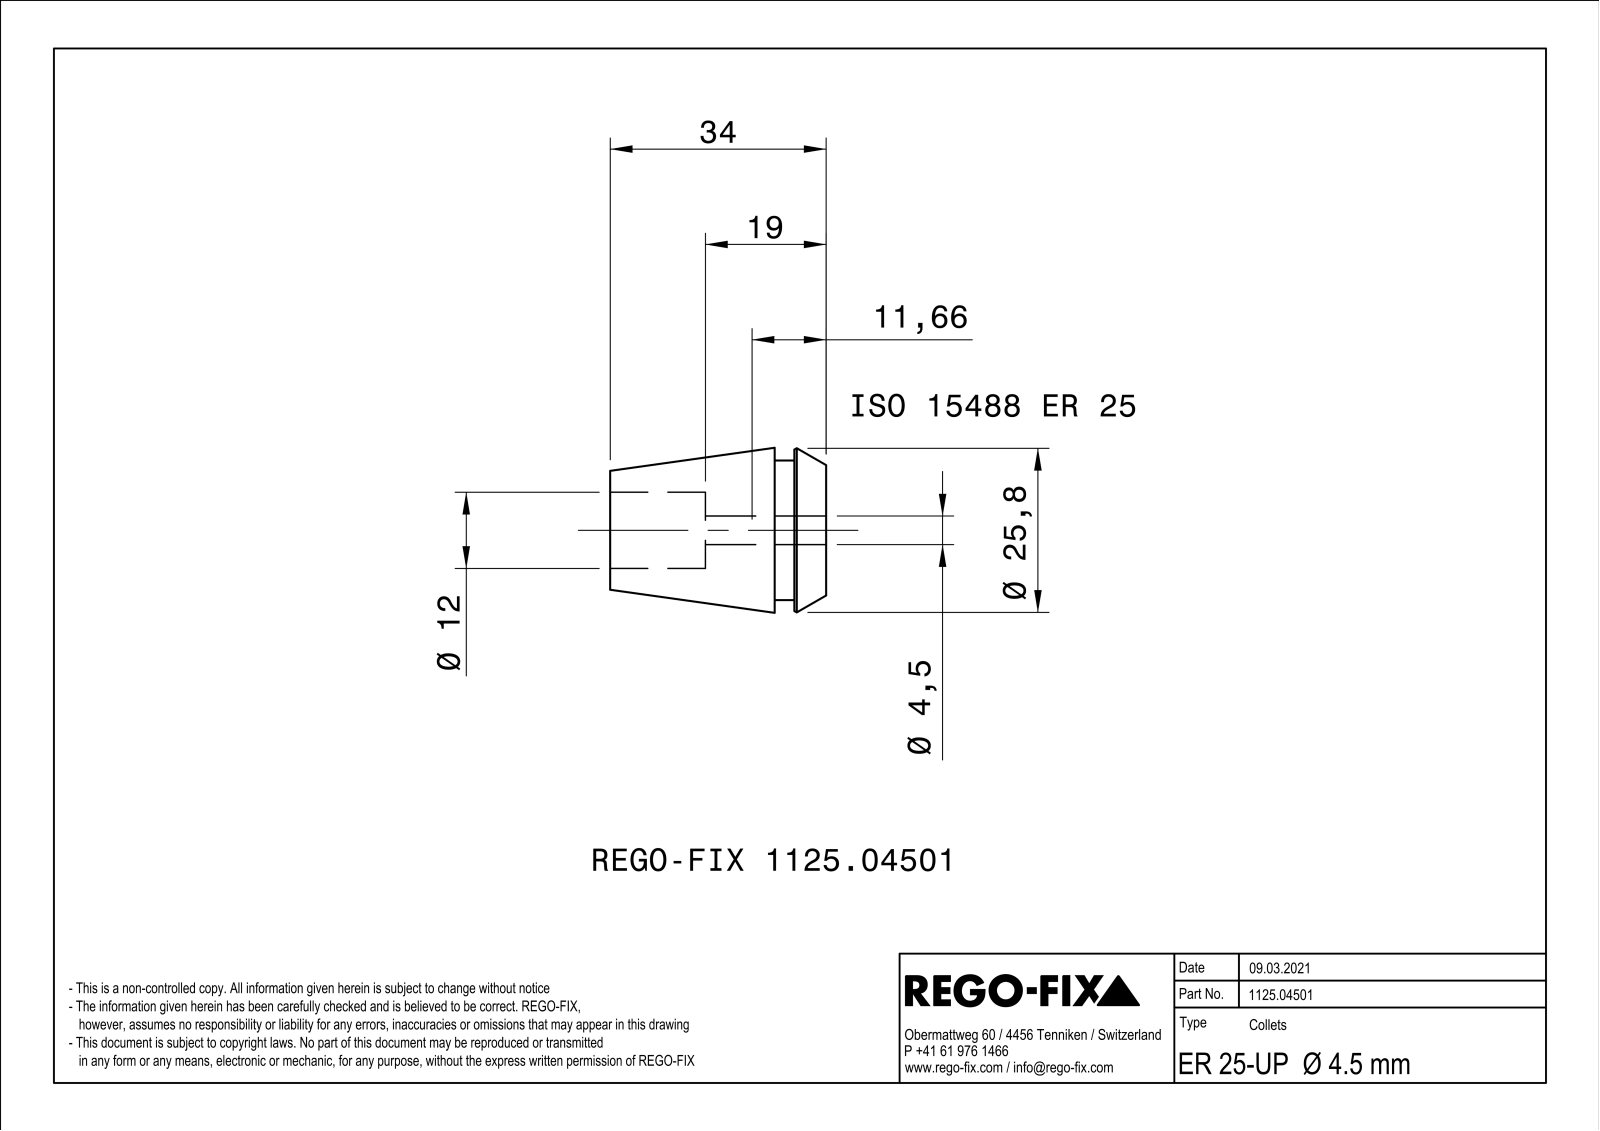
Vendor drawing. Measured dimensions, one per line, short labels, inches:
name: NOCUT
written by: SIEMENS PLM Software Solid Edge ST10 (AUTOMOTIVE_DESIGN)
unit: in
bodies: 1 solid, 272 faces (104 planar, 48 cylindrical, 120 other)
size: 1.339 × 1.023 × 1.023
volume: 0.602 in³; area: 14.46 in²
holes: 1× ⌀0.472
bosses: 1× ⌀0.866
rounds: 8× R1.575, 1× R0.089
face distances: 0.024, 0.024, 0.023, 0.319, 1.339, 1.02, 0.197, 0.122, 1.142, 0.748
